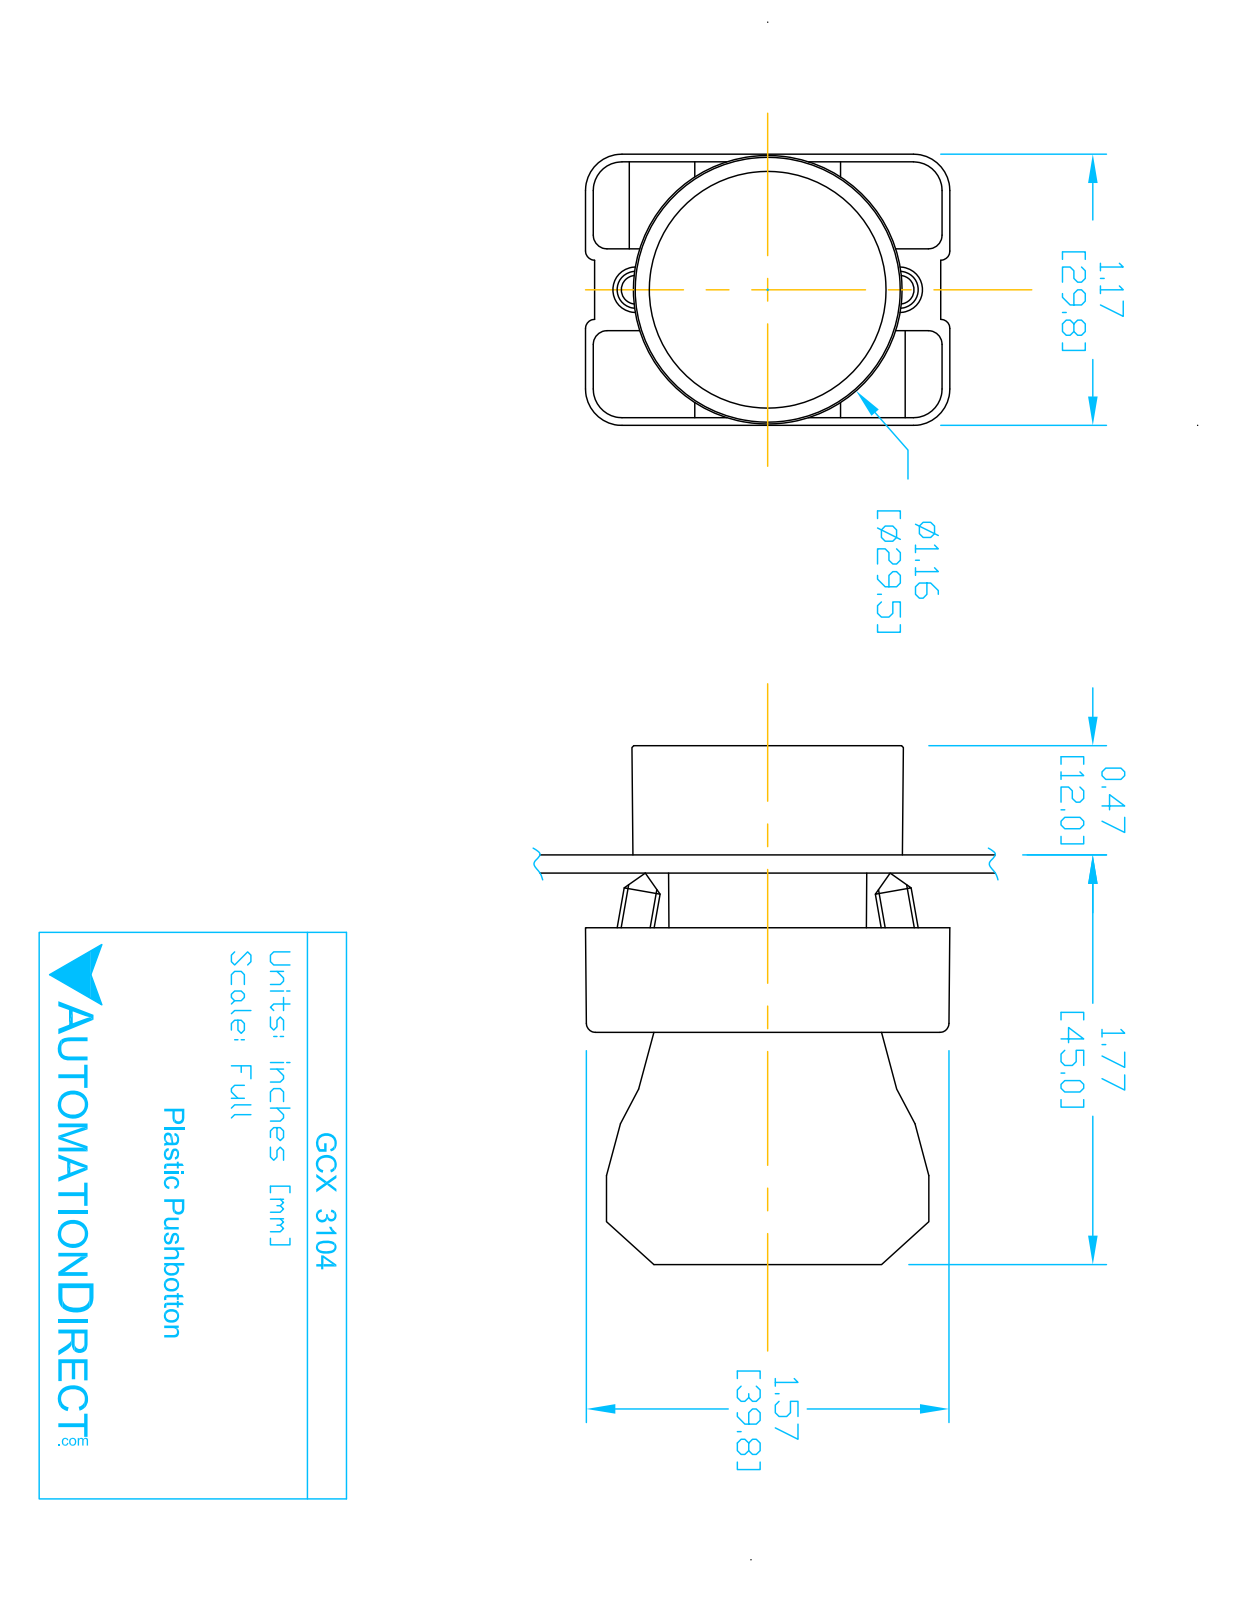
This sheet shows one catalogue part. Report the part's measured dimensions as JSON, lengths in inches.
{"part_name": "ecx1040; ECX3029-2; GCX3104 OPERATOR; GCX3104", "step_written_by": "SolidWorks 2016 (AUTOMOTIVE_DESIGN)", "units": "inches", "bodies": {"solids": 6, "faces": 381, "planar": 222, "cylindrical": 132, "other": 27}, "overall_size": [2.217, 1.581, 1.177], "volume_in3": 1.741, "surface_area_in2": 27.14, "round_holes": [[0.079, 2], [0.124, 2], [0.13, 2], [0.087, 1], [0.197, 1], [0.878, 1], [0.888, 1], [1.024, 1]], "round_bosses_or_shafts": [[0.157, 2], [1.175, 1], [1.004, 1], [0.945, 1], [0.856, 1], [0.78, 1]], "partial_cylinders_radius": [[0.059, 24], [0.041, 12], [0.124, 12], [0.157, 12], [0.039, 4], [0.128, 2], [0.02, 1], [0.063, 1]], "face_to_face_distances": [0.72, 0.579, 0.033, 0.472, 1.193, 0.031, 0.689, 0.598, 1.161, 1.071], "hole_center_spacings": [0.236, 0.544, 0.472, 0.49]}
